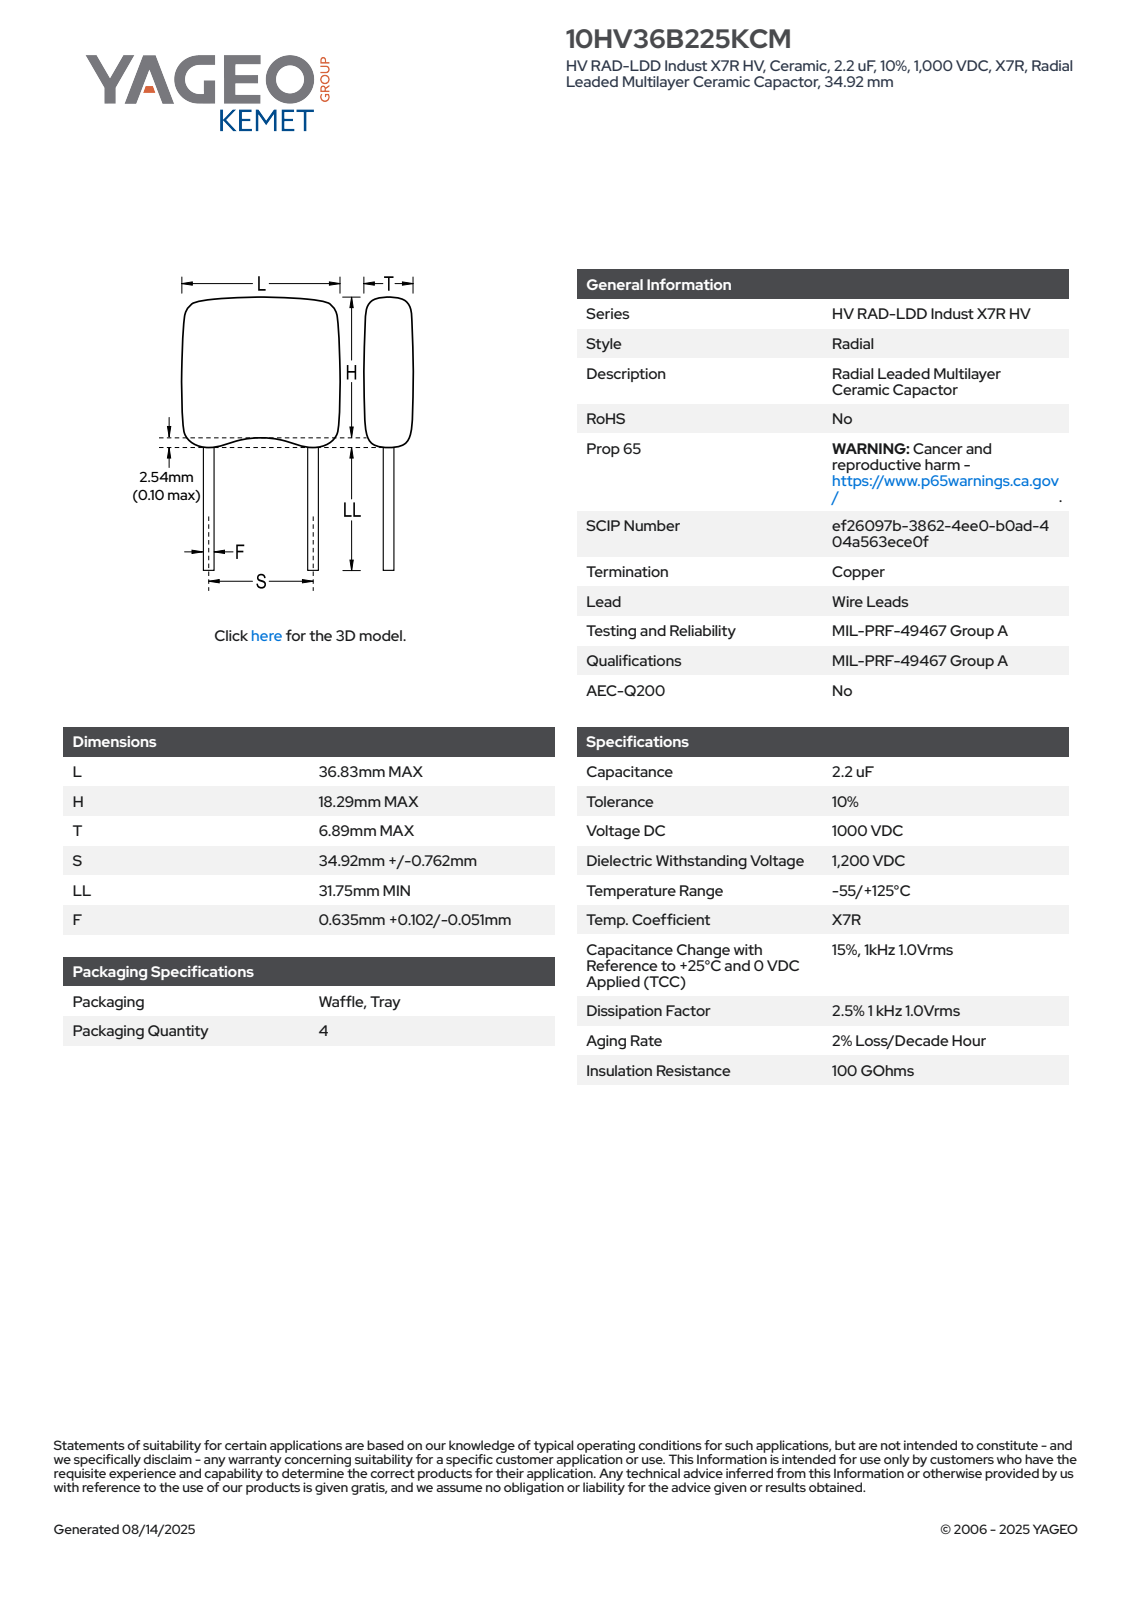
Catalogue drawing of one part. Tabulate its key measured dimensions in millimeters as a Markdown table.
| quantity | value |
| --- | --- |
| part name | CCRM_RCST_HV36_L36.83H18.29T6.89S34.92LL31.75F0.737 |
| STEP written by | SolidWorks 2021 (AUTOMOTIVE_DESIGN) |
| units | millimeters |
| bodies | 4 solids, 98 faces (66 planar, 20 cylindrical, 12 other) |
| overall size | 36.83 × 23.05 × 6.89 |
| volume | 4 736 mm³ |
| surface area | 2 236 mm² |
| round bosses / shafts (diameter × count) | 0.74 × 2 |
| partial cylindrical surfaces (radius × count) | 1 × 8, 0.5 × 4 |
| main face-to-face distances | 6.89, 36.83, 19.87, 3.17, 23.04, 6.39, 16.65, 13.48, 11.97, 8.8 |
